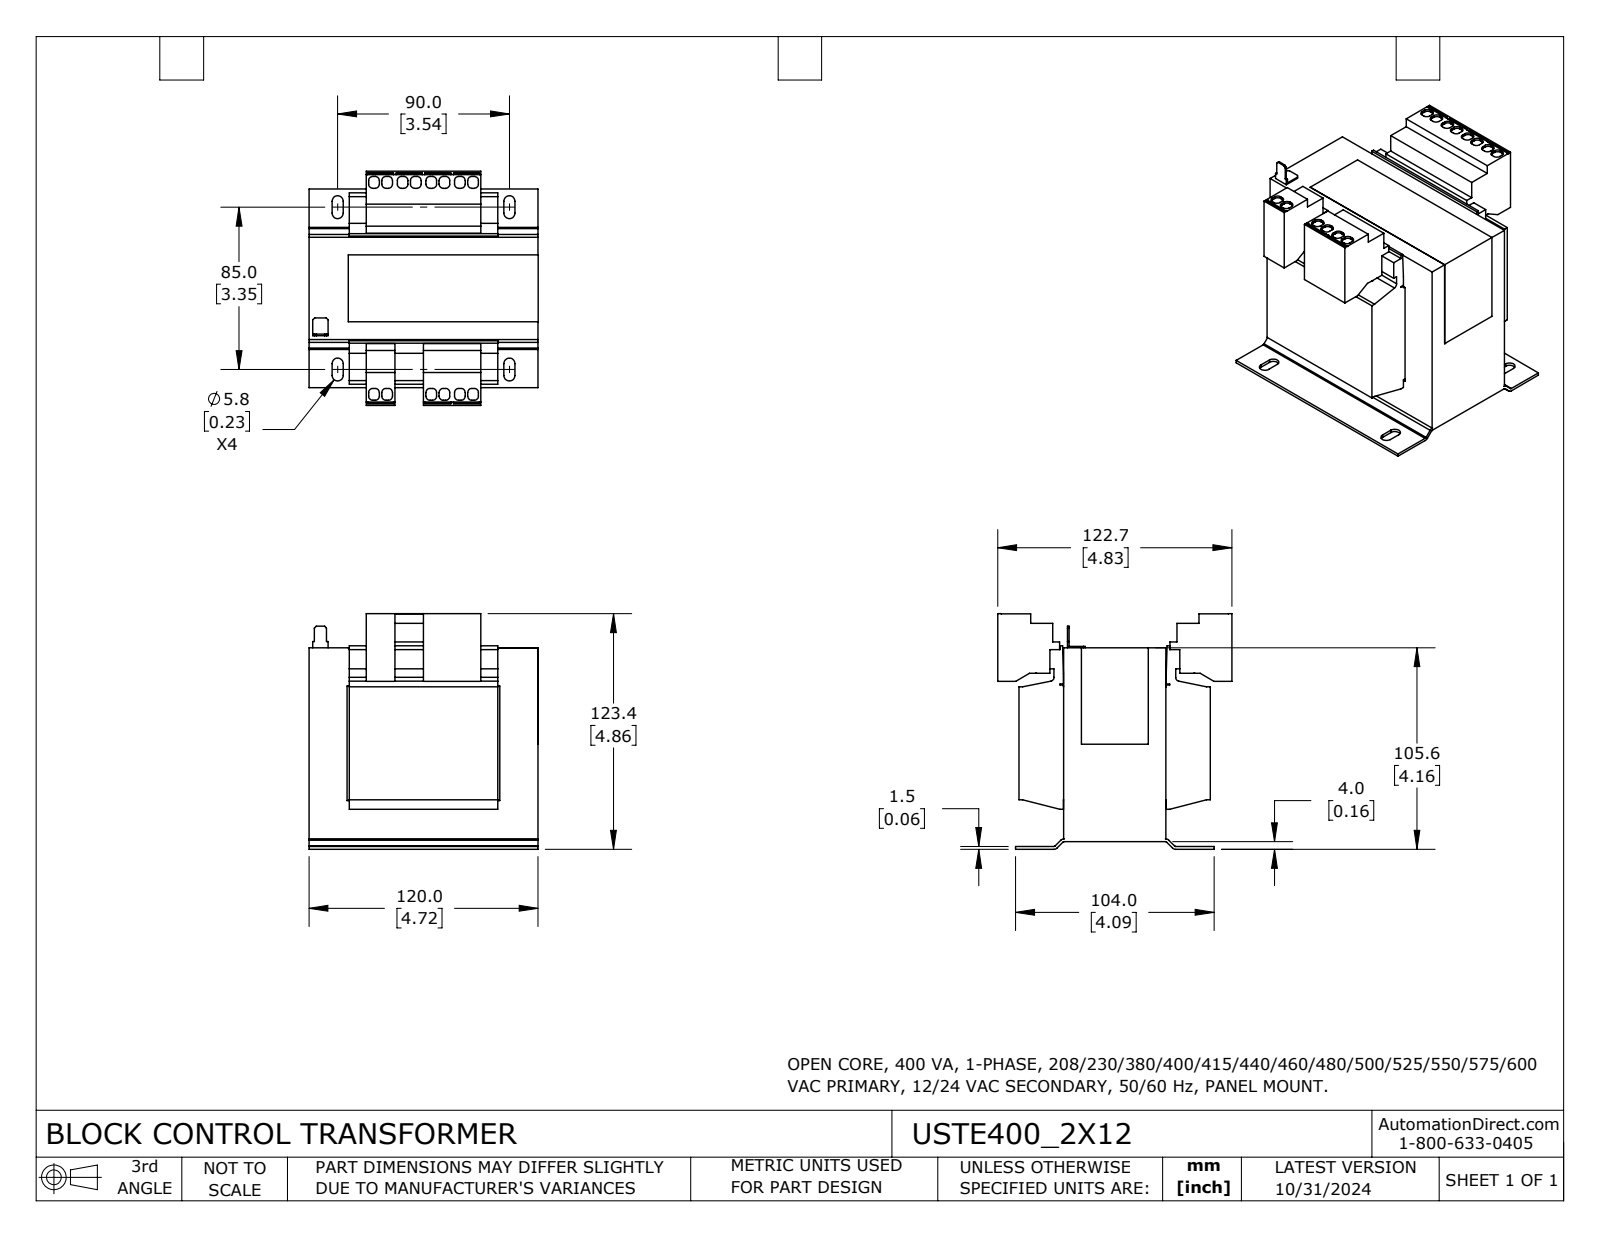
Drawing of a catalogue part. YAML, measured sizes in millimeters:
part_name: "USTE400_2X12"
step_written_by: "SolidWorks 2023 (CONFIG_CONTROL_DESIGN)"
units: millimeters
bodies: {solids: 1, faces: 434, planar: 356, cylindrical: 78, other: 0}
overall_size: [123.4, 122.7, 120]
volume: 974900
surface_area: 130600
partial_cylinders:
  - {radius: 2.2, count: 56}
  - {radius: 2.9, count: 8}
  - {radius: 1, count: 4}
  - {radius: 2.5, count: 4}
  - {radius: 2, count: 2}
face_to_face_distances: [21.2, 98.9, 20, 53.6, 30, 100, 1.1, 78.8, 77.7, 1.5]
